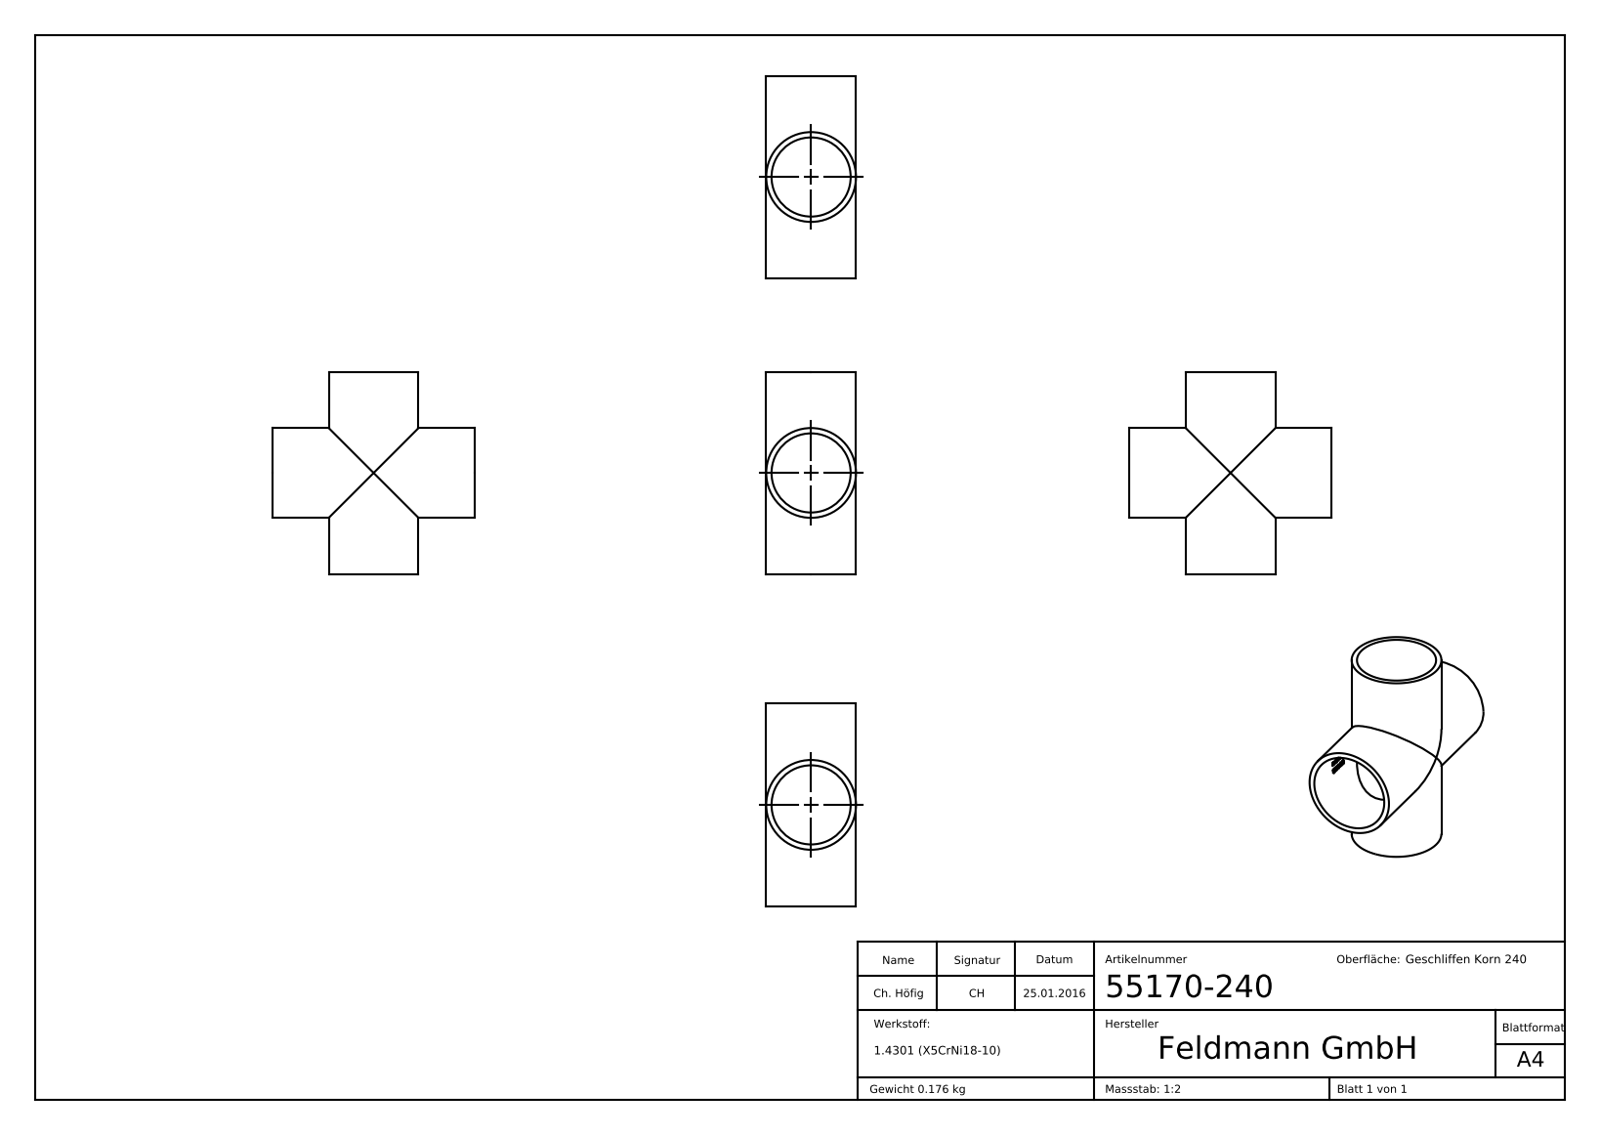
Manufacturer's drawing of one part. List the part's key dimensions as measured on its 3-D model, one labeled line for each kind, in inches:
Part name (STEP PRODUCT): 55170-240
STEP written by: SolidWorks 2015 (CONFIG_CONTROL_DESIGN)
Units: inches
Bodies: 1 solid, 241 faces (105 planar, 48 cylindrical, 88 other)
Overall size (bounding box): 2.992 × 2.992 × 1.327
Volume: 1.356 in³ · Surface area: 35.67 in²
Round holes (diameter × count): ⌀1.169 ×2
Round bosses / shafts (diameter × count): ⌀1.327 ×2
Partial cylindrical surfaces — rounded edges, fillets, slot ends (radius × count): R0.589 ×1
Main face-to-face distances: 2.992, 0.015, 0.05, 0.167, 0.08, 1.496, 0.117, 0.144, 0.052, 0.129
